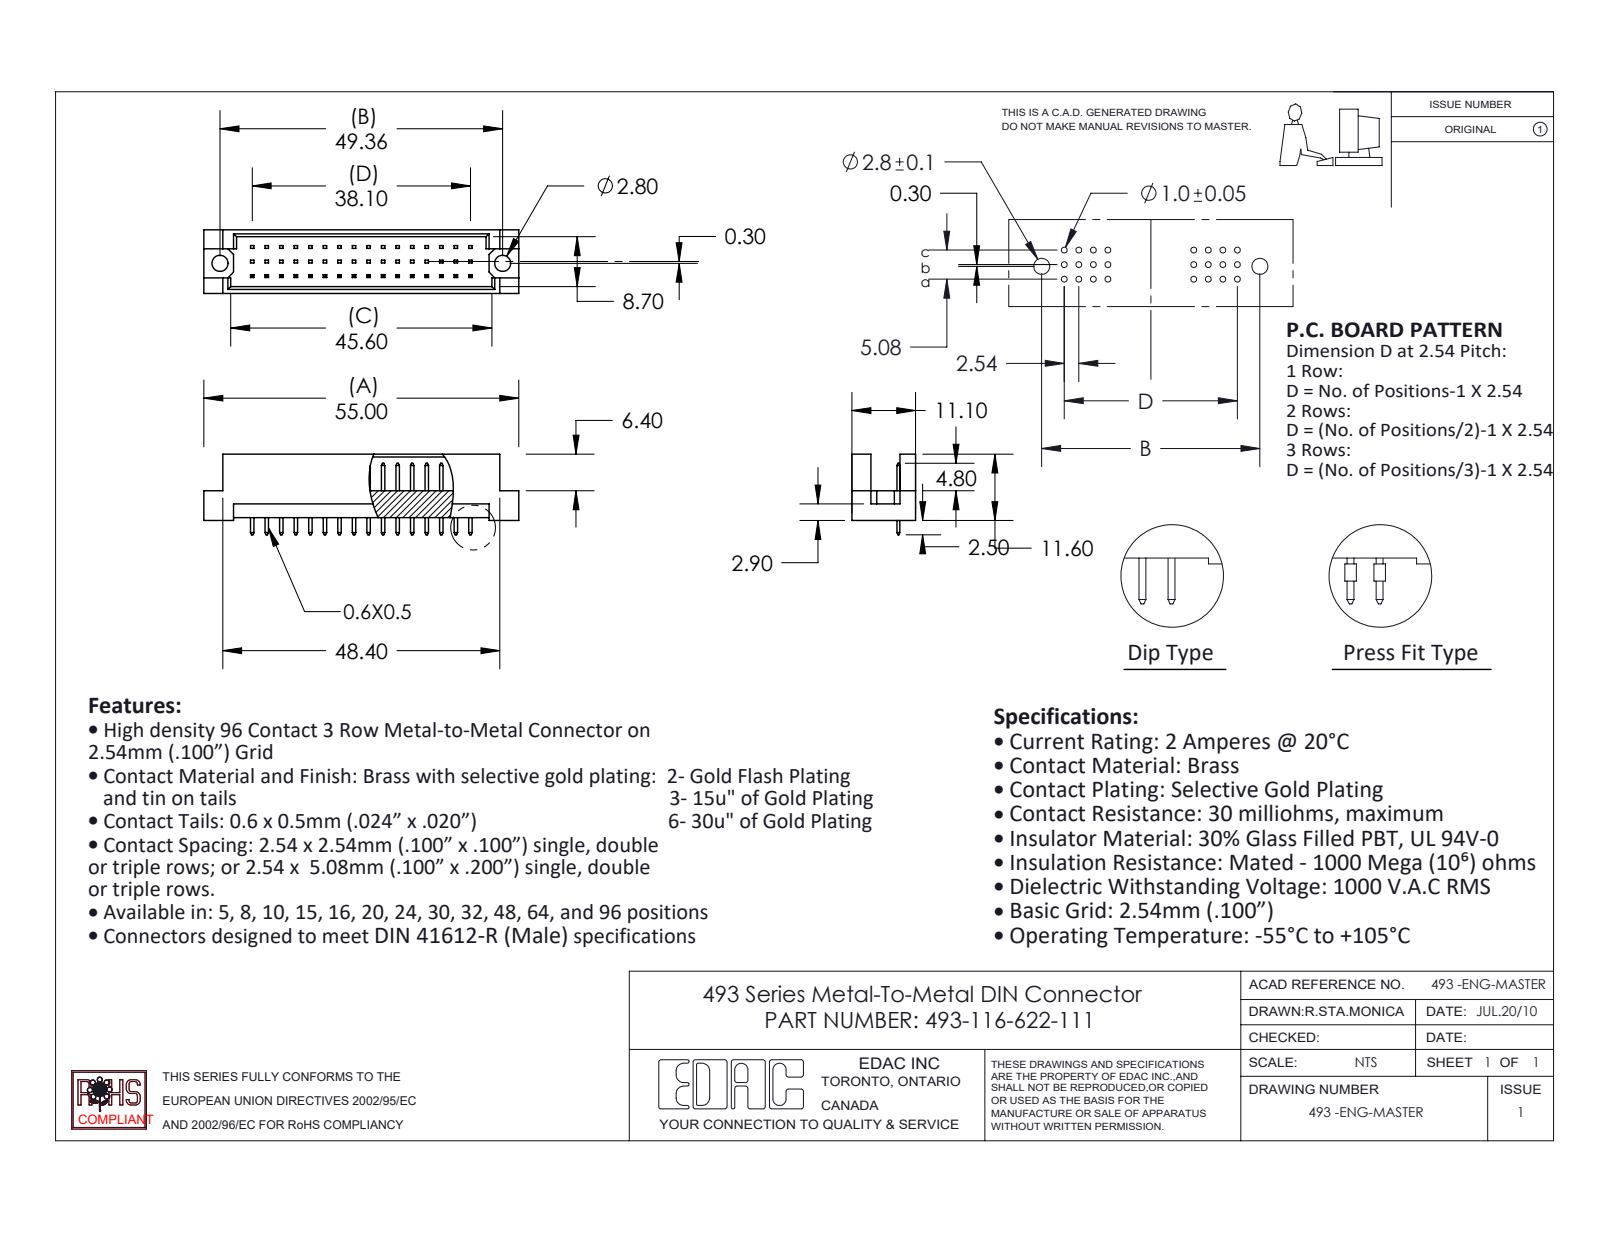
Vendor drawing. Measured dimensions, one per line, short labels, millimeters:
name: 493 Part_48; 493-116-622-111; 493-290_22
written by: SolidWorks 2020 (CONFIG_CONTROL_DESIGN)
unit: mm
bodies: 17 solids, 468 faces (464 planar, 4 cylindrical, 0 other)
size: 55 × 14.1 × 11.1
volume: 3 331 mm³; area: 4 190 mm²
holes: 2× ⌀2.8
face distances: 1.2, 9.9, 11.1, 8.7, 4.7, 0.5, 2.54, 5.08, 2.76, 8.34
hole spacings: 49.36
